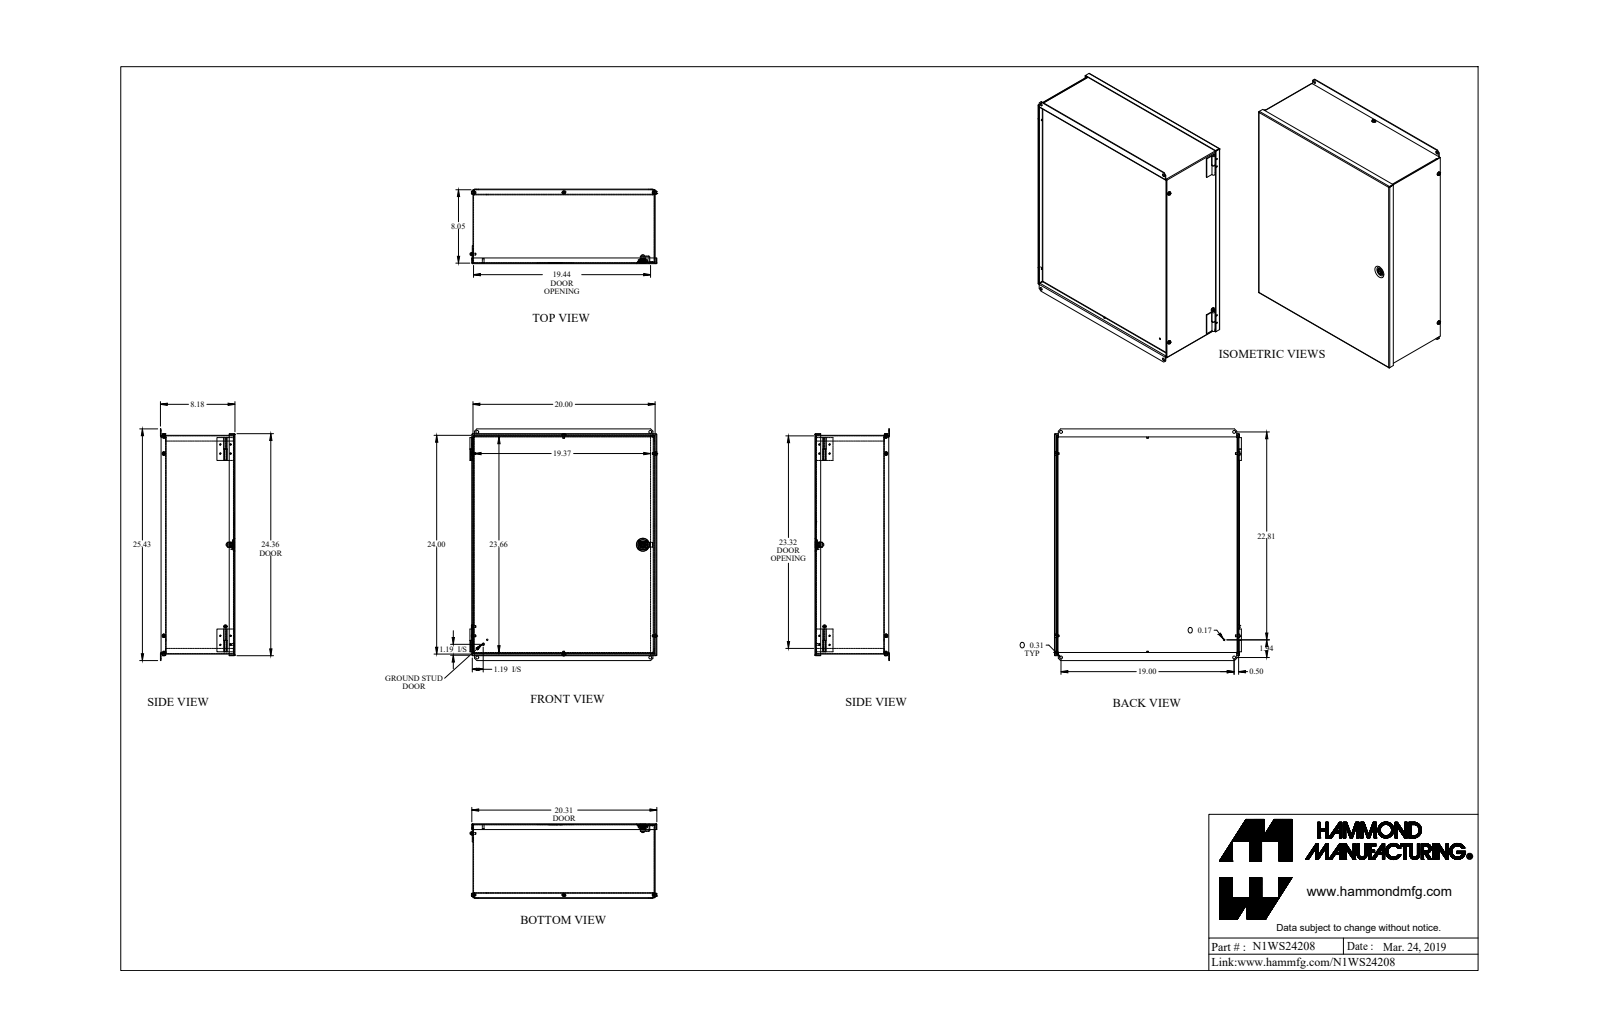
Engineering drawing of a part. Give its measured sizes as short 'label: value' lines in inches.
name: N1WS24208
written by: SolidWorks 2018 (AUTOMOTIVE_DESIGN)
unit: in
bodies: 17 solids, 607 faces (328 planar, 214 cylindrical, 65 other)
size: 25.425 × 20.519 × 8.179
volume: 112.6 in³; area: 3 676 in²
holes: 8× ⌀0.14, 5× ⌀0.17, 4× ⌀0.312, 1× ⌀0.187, 1× ⌀0.319, 1× ⌀0.476
bosses: 8× ⌀0.128, 4× ⌀0.19, 3× ⌀0.375, 1× ⌀0.787, 1× ⌀0.547, 1× ⌀0.472, 1× ⌀0.469, 1× ⌀0.375
rounds: 9× R0.029, 9× R0.086, 8× R0.036, 6× R0.108, 6× R0.109, 4× R0.012, 4× R0.1, 2× R0.079
face distances: 0.057, 0.072, 0.057, 7.564, 7.621, 7.492, 7.549, 19.943, 23.943, 19.886
hole spacings: 1, 1.119, 1.501, 21, 21.03, 20, 6.195, 6.275
